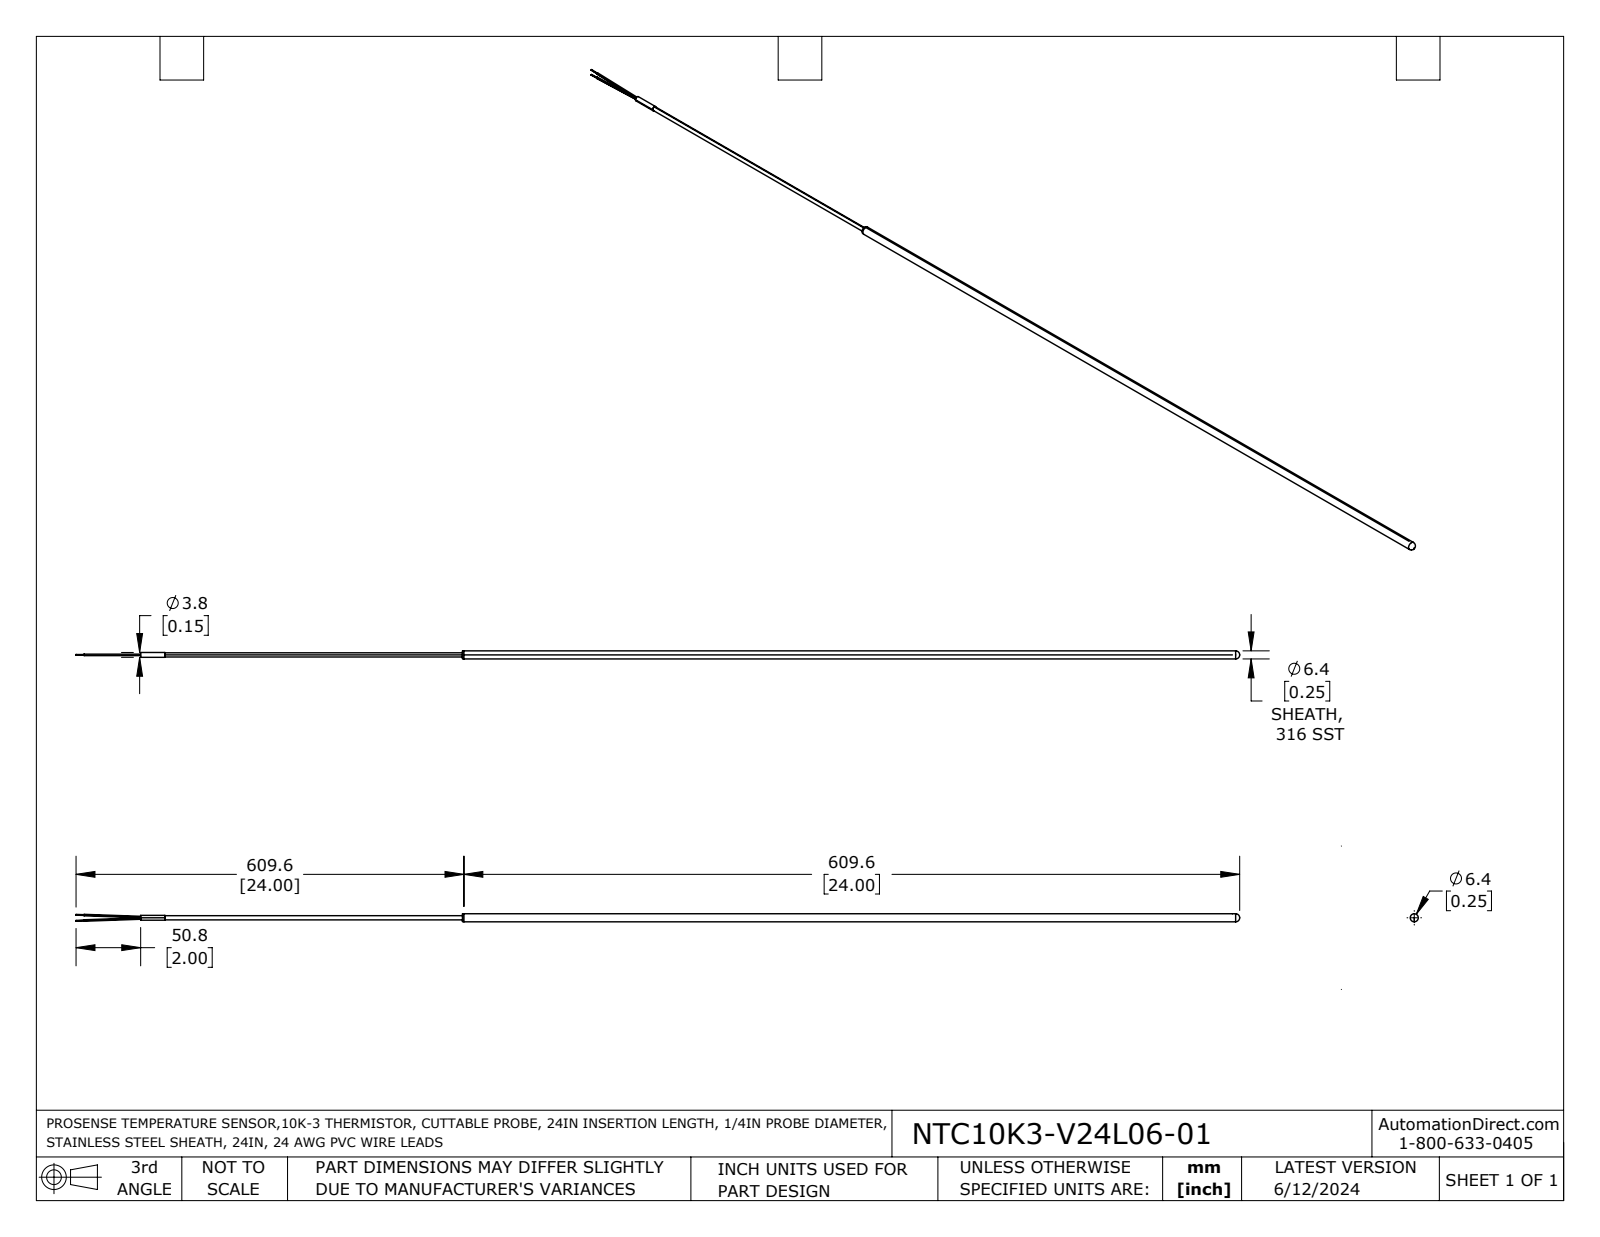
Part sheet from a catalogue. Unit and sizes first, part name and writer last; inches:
Units: inches
Overall size (bounding box): 36 × 0.25 × 0.25
Round holes (diameter × count): ⌀0.115 ×1, ⌀0.131 ×1
Round bosses / shafts (diameter × count): ⌀0.25 ×1, ⌀0.235 ×1, ⌀0.15 ×1, ⌀0.145 ×1, ⌀0.13 ×1
Main face-to-face distances: 0.046, 9.955, 10.001, 10.188, 0.233, 0.187, 0.751, 9.204, 9.25, 9.437
Volume: 1.321 in³ · Surface area: 24.49 in²
Bodies: 3 solids, 35 faces (12 planar, 14 cylindrical, 9 other)
Part name (STEP PRODUCT): NTC10K3-V24L06-01
STEP written by: SolidWorks 2021 (AUTOMOTIVE_DESIGN)
